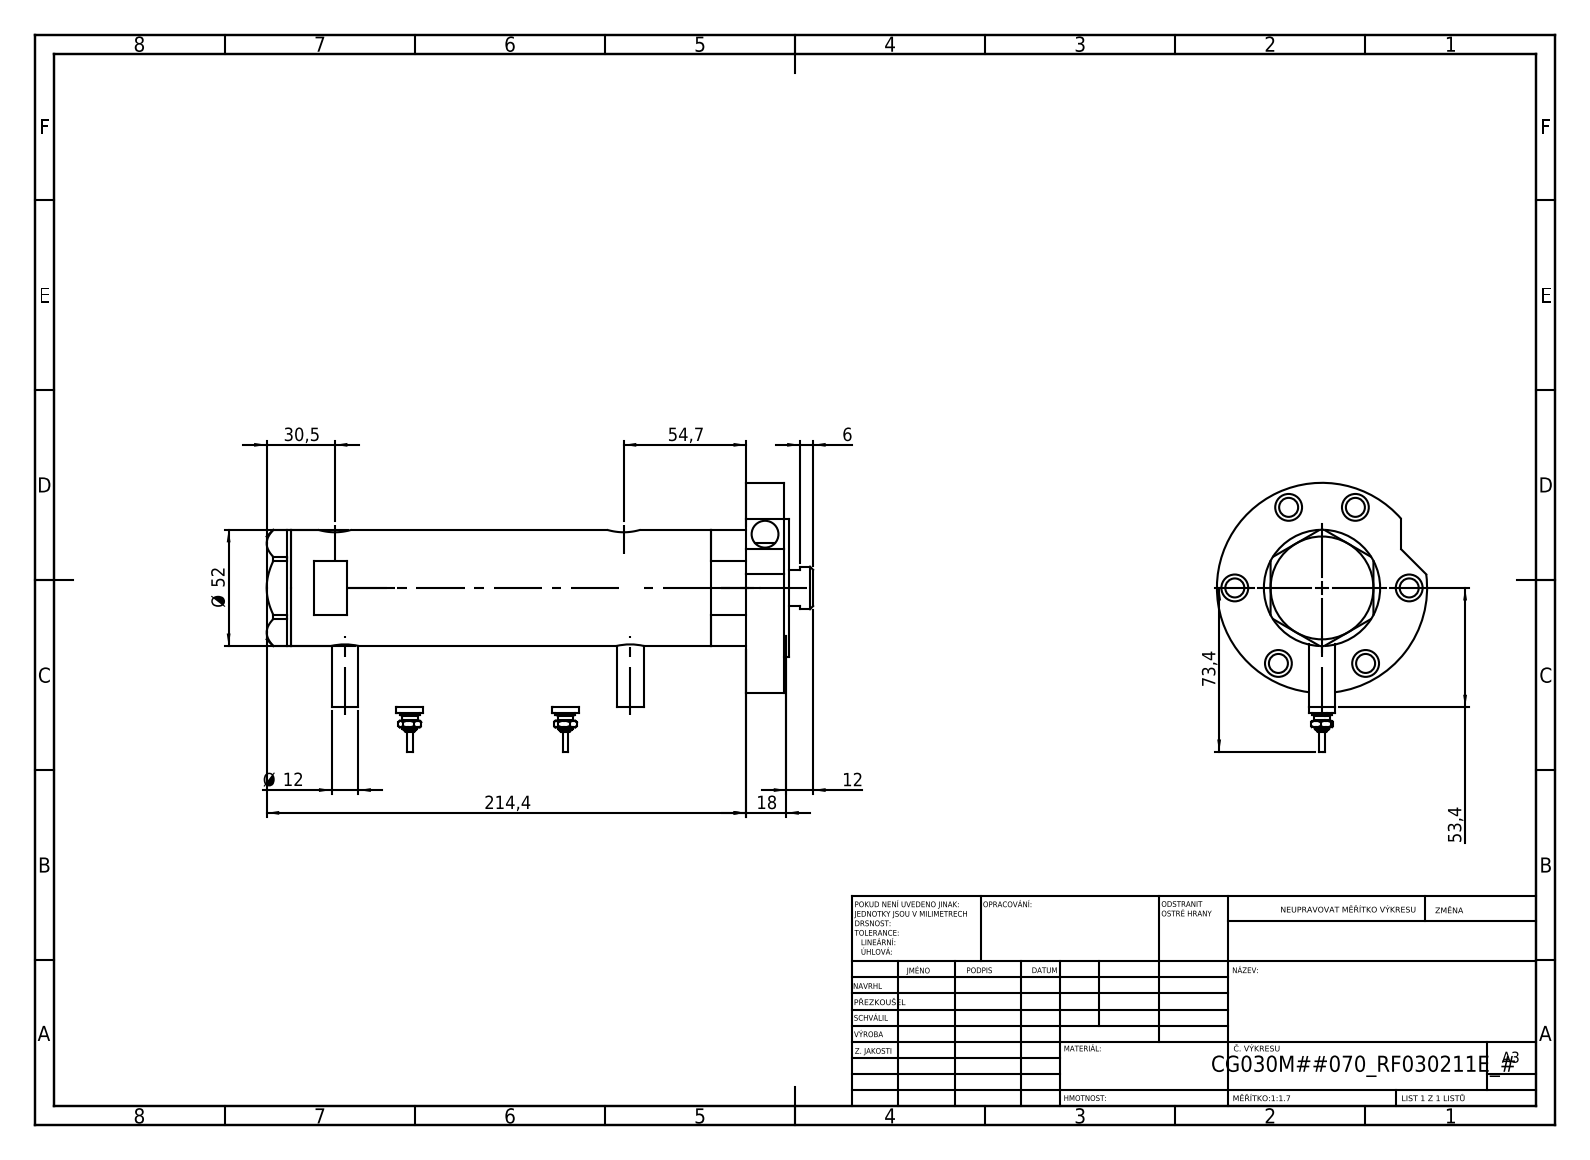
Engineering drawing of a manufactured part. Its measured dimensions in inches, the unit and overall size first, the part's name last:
Units: inches
Overall size (bounding box): 9.622 × 4.74 × 3.701
Round holes (diameter × count): ⌀0.472 ×7, ⌀0.335 ×6, ⌀0.383 ×2, ⌀0.492 ×2, ⌀0.591 ×2, ⌀0.256 ×1, ⌀0.787 ×1, ⌀0.846 ×1, ⌀1.181 ×1, ⌀1.299 ×1, ⌀1.575 ×1, ⌀1.732 ×1
Round bosses / shafts (diameter × count): ⌀0.472 ×4, ⌀0.354 ×2, ⌀0.276 ×2, ⌀0.177 ×2, ⌀0.098 ×2, ⌀3.701 ×1, ⌀2.441 ×1, ⌀2.047 ×1
Main face-to-face distances: 0.669, 8.008, 8.677, 0.079, 8.756, 5.965, 2.043, 2.713, 0.433, 9.189
Hole centre spacings: 1.535, 1.706, 2.553, 2.659, 2.754, 3.064, 0.114, 0.177
Volume: 32.61 in³ · Surface area: 191.5 in²
Bodies: 7 solids, 270 faces (104 planar, 102 cylindrical, 64 other)
Part name (STEP PRODUCT): V270CG_VC; V270CG_RF211E; V270CG_MIDDLE; V270CG_BACK (+2 more)
STEP written by: SolidWorks 2019 (CONFIG_CONTROL_DESIGN)
